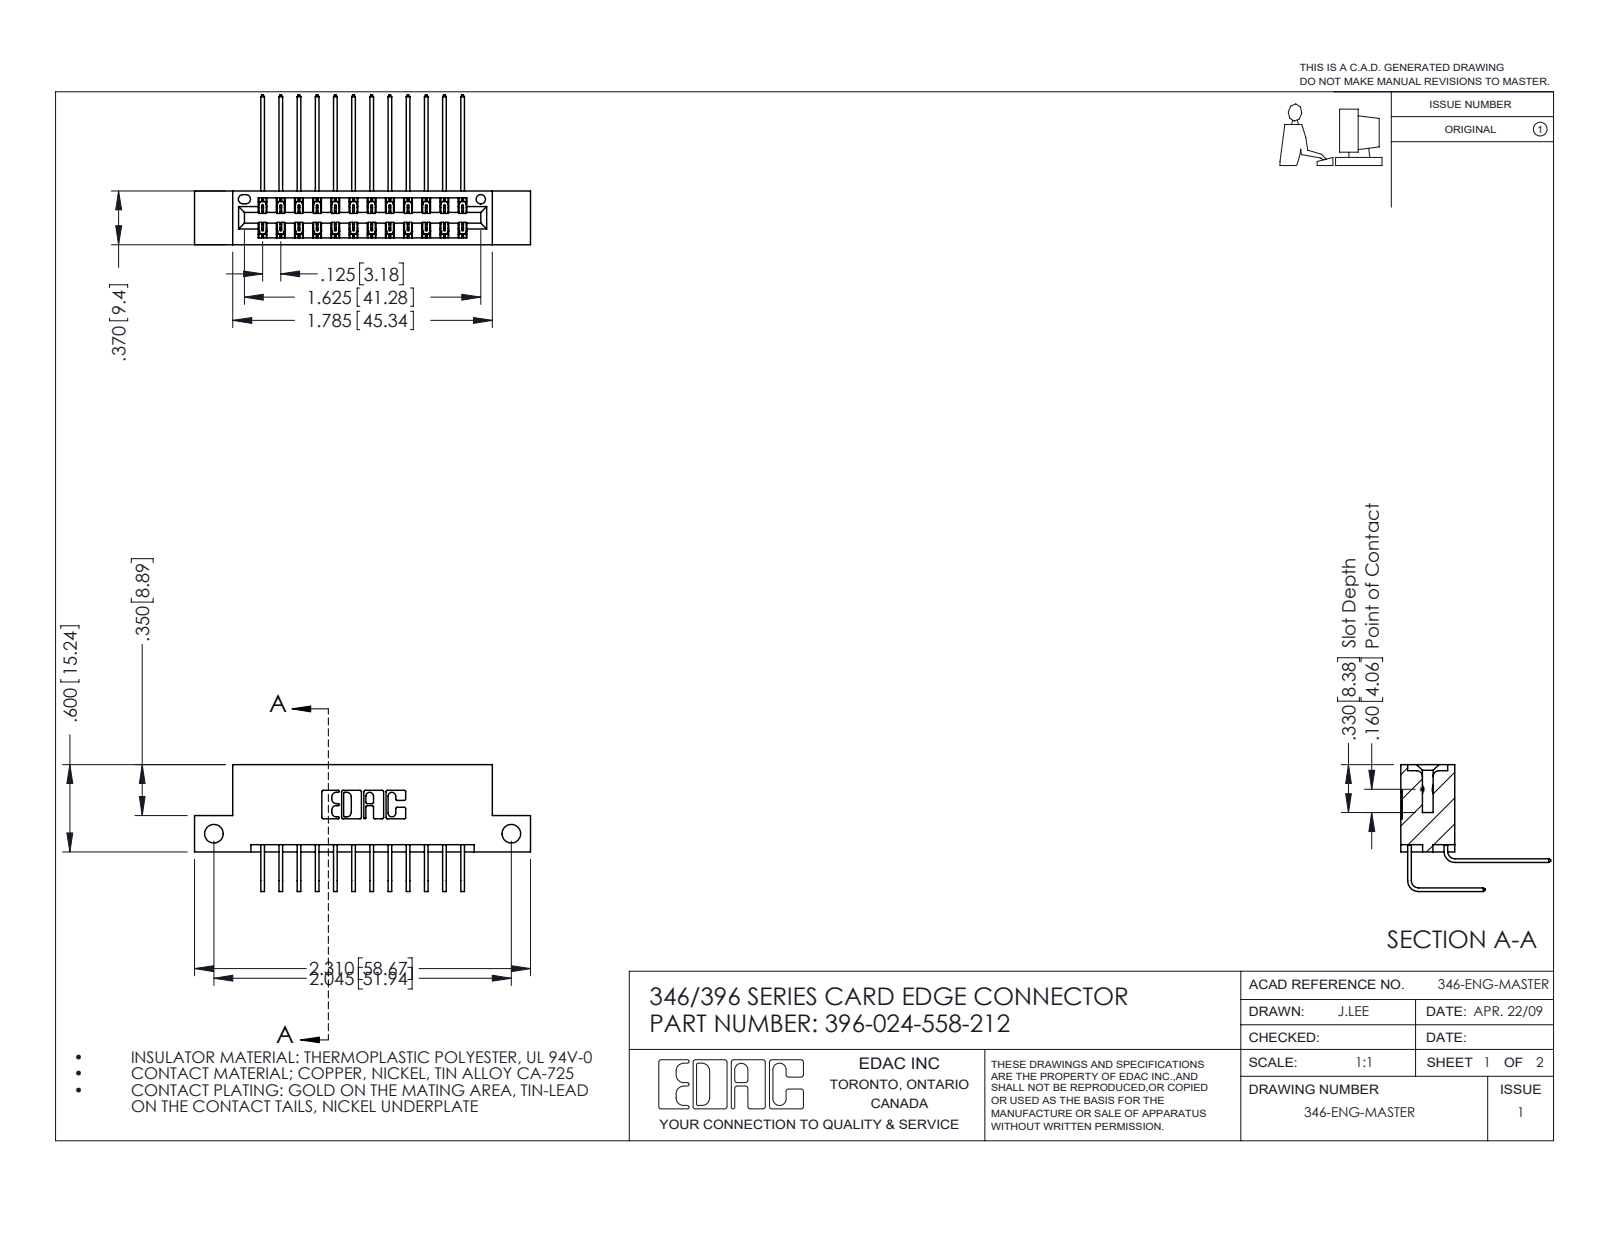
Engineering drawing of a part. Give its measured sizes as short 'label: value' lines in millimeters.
name: 346 Part_Flush Mounting Lugs - Side Mount; 345-292-001_558 Tail - 2; 396-024-558-212; 345-292-001_558 559 Tail - 1
written by: SolidWorks 2016 (CONFIG_CONTROL_DESIGN)
unit: mm
bodies: 25 solids, 1418 faces (964 planar, 454 cylindrical, 0 other)
size: 58.7 × 26.2 × 22.2
volume: 5 540 mm³; area: 7 671 mm²
holes: 2× ⌀3.3, 1× ⌀1.6
rounds: 36× R0.2, 22× R0.3, 6× R0.2, 6× R0.8, 3× R0.7, 2× R0.4, 2× R0.6, 2× R0.6
face distances: 8.2, 1.2, 6.4, 9.4, 7.6, 0.6, 1.8, 7, 3.8, 5.6
hole spacings: 51.9
